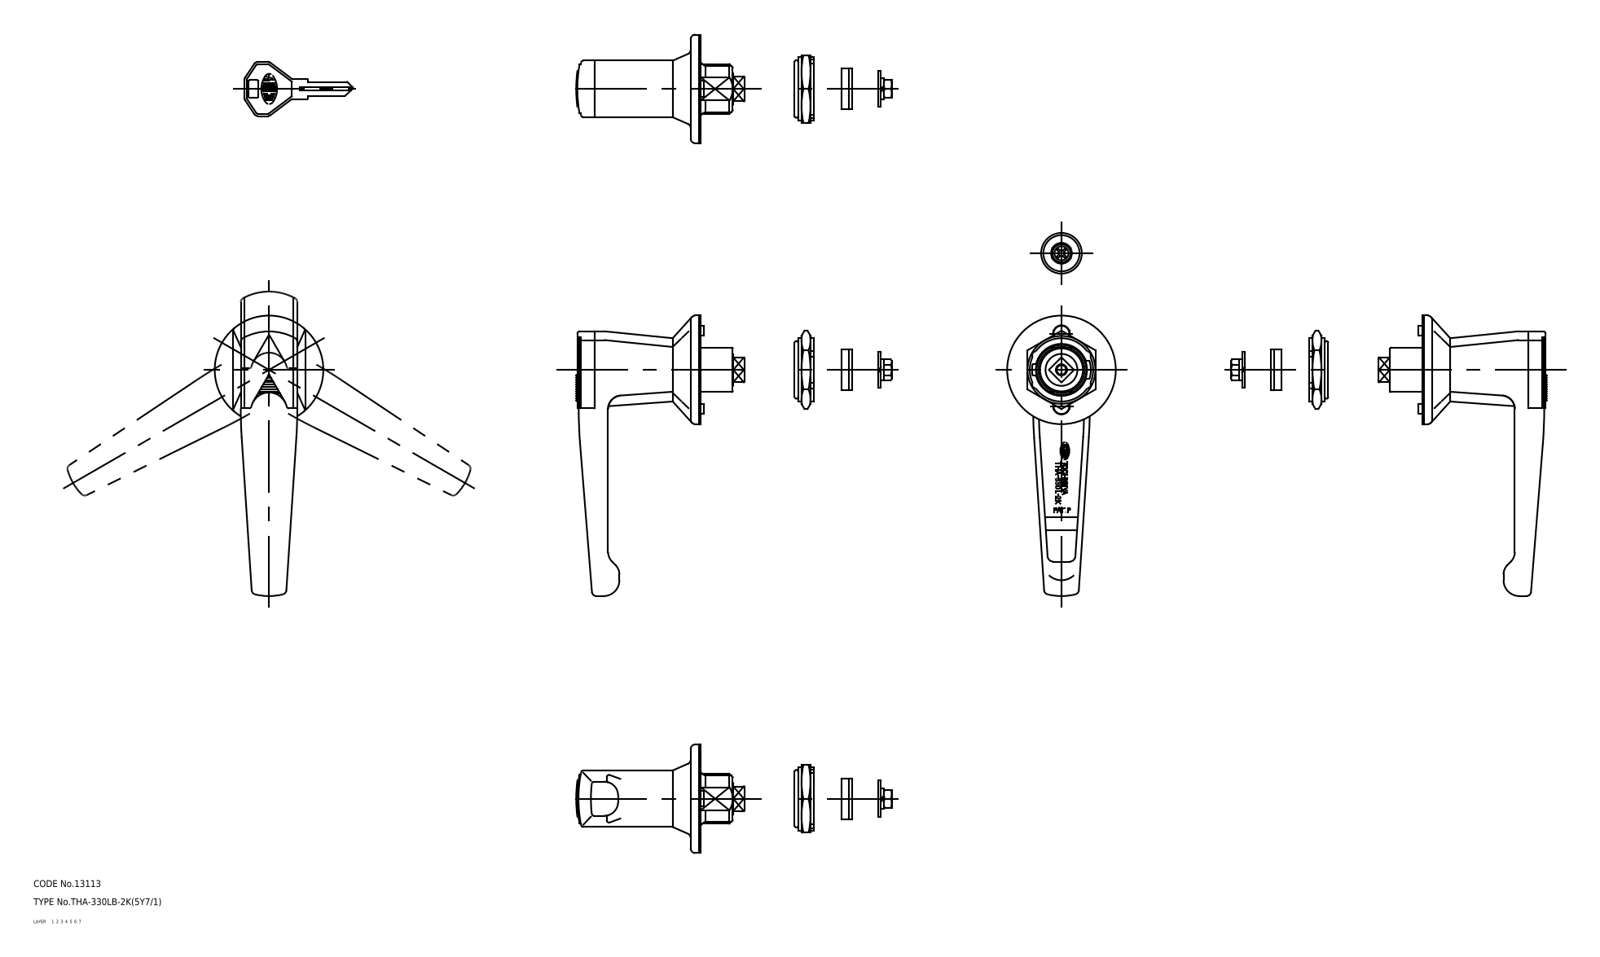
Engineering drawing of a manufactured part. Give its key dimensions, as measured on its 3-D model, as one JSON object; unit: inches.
{"part_name": "key; washer_D; washer_C; washer_B (+8 more)", "step_written_by": "CADfix (AUTOMOTIVE_DESIGN)", "units": "inches", "bodies": {"solids": 11, "faces": 378, "planar": 0, "cylindrical": 0, "other": 378}, "overall_size": [5.576, 4.882, 1.89], "volume_in3": 3.997, "surface_area_in2": 47.97}
